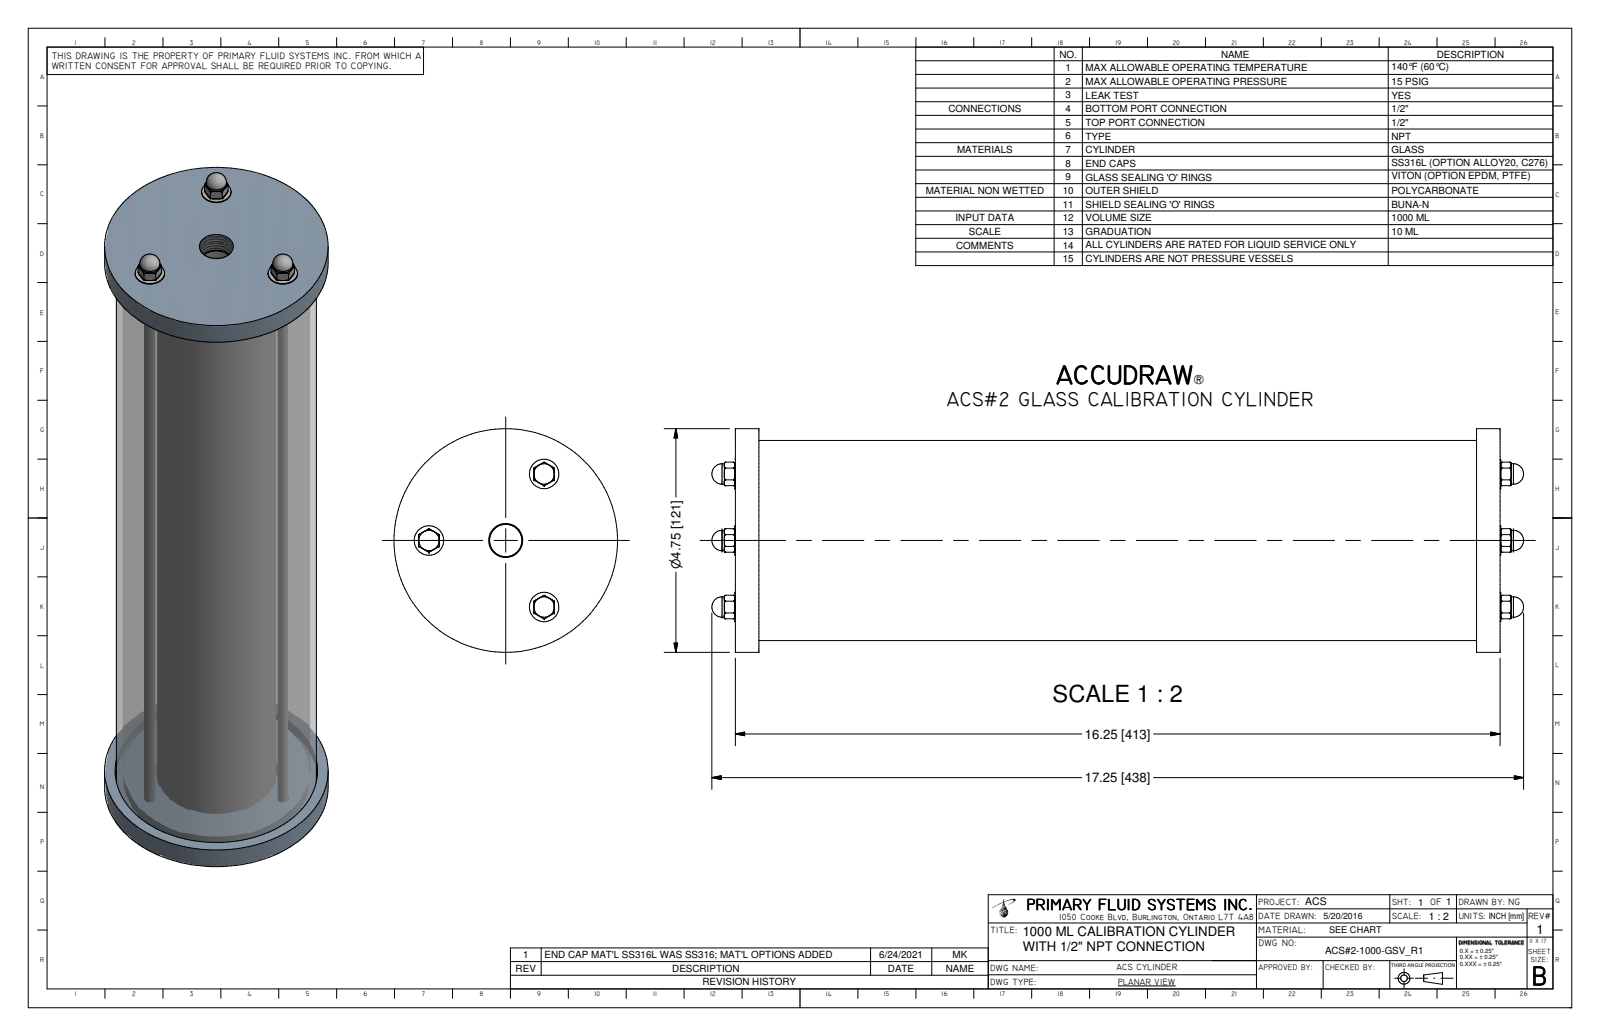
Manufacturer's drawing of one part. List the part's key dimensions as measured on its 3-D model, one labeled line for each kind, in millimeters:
Part name (STEP PRODUCT): ACS#2-1000-GSV_R0; ACS-3-1000-METAL_R3; ACS-2-1000-PC_R6; ACS-1-1000-A_R0 (+3 more)
STEP written by: Autodesk Inventor 2009 (AUTOMOTIVE_DESIGN)
Units: millimetres
Bodies: 19 solids, 429 faces (38 planar, 41 cylindrical, 350 other)
Overall size (bounding box): 438.2 × 120.7 × 120.7
Volume: 884 700 mm³ · Surface area: 523 500 mm²
Round holes (diameter × count): ⌀4.6 ×3, ⌀6.8 ×3, ⌀7.1 ×3, ⌀59.2 ×1, ⌀66 ×1, ⌀101.6 ×1, ⌀109.2 ×1
Round bosses / shafts (diameter × count): ⌀15.9 ×3, ⌀6.4 ×3, ⌀120.7 ×1, ⌀108 ×1, ⌀100.3 ×1, ⌀64 ×1, ⌀55.9 ×1
Main face-to-face distances: 12.7, 400.1, 412.8, 387.4, 394.3, 5.7, 407, 7, 409.6, 2.5
Hole centre spacings: 41.4, 71.8
